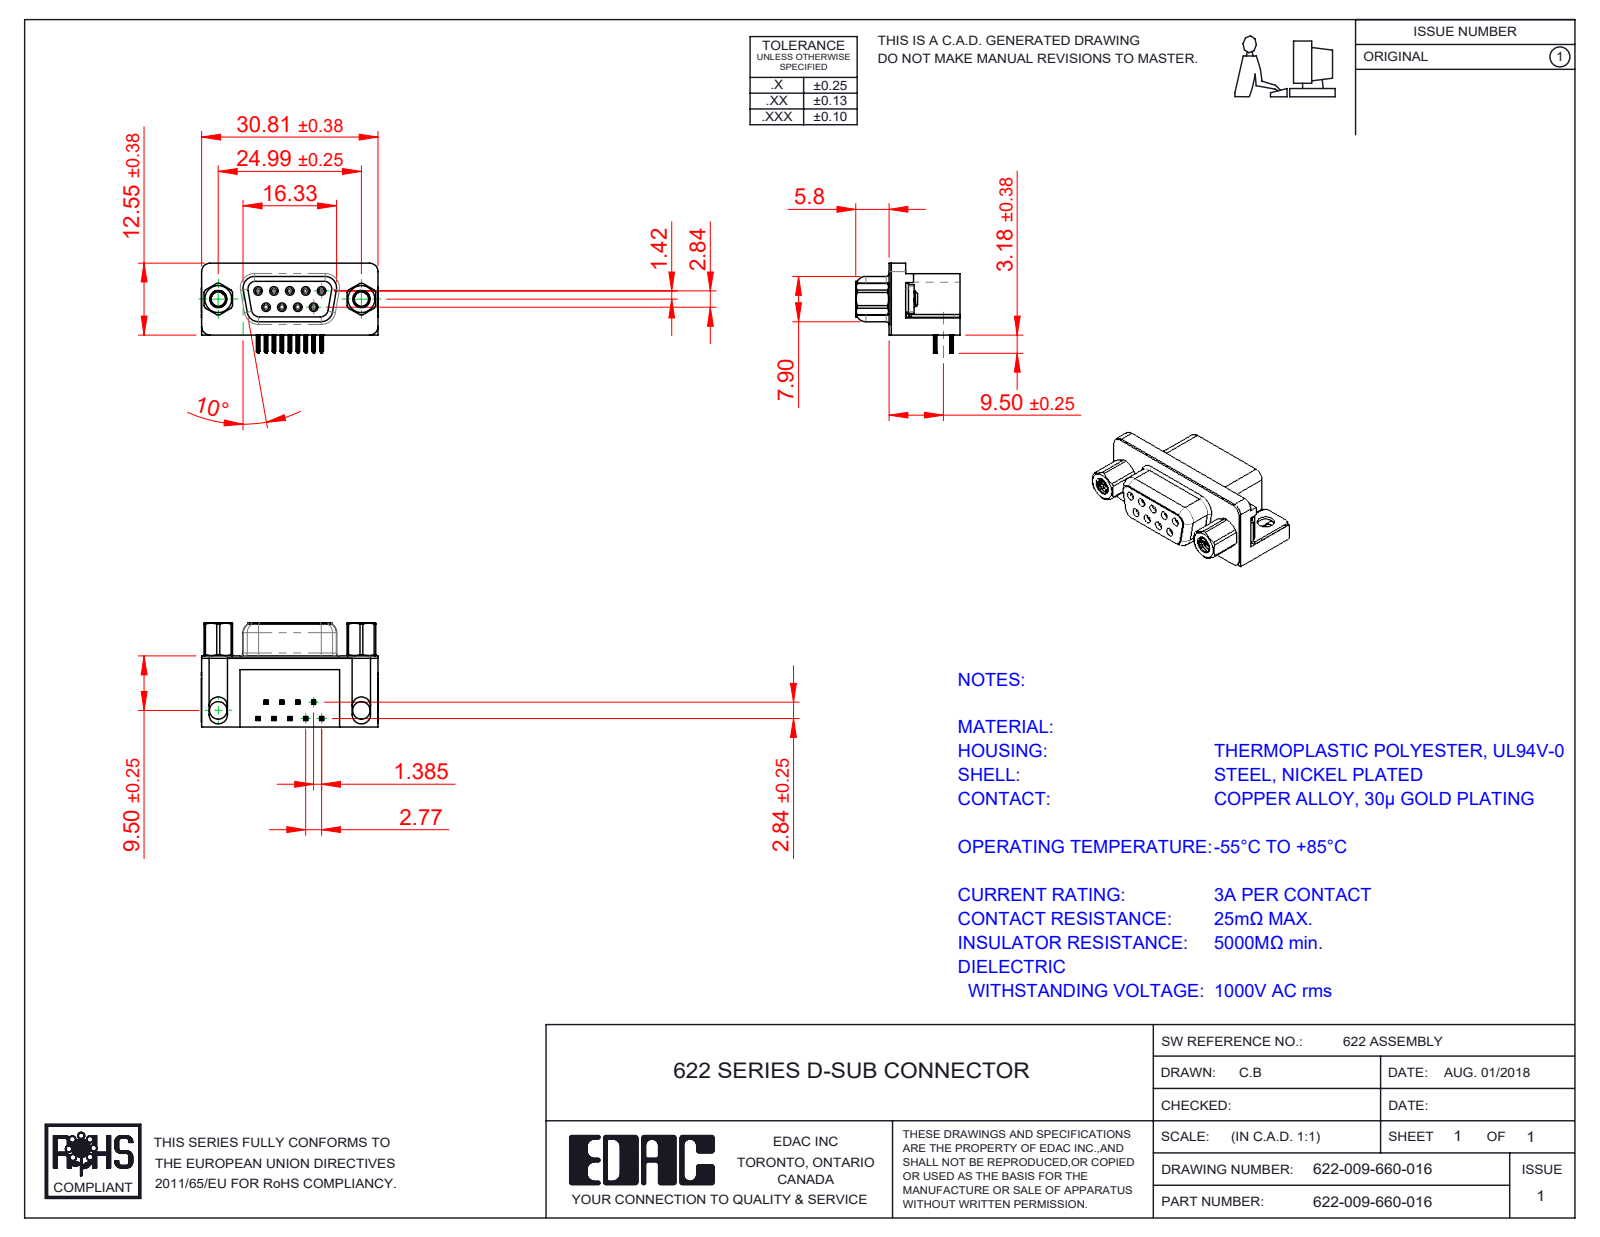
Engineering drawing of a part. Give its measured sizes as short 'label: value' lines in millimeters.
name: 622 Shell_9 Socket; 622 Contact Top; 622 Thru Hole Board Mount; 622-009-660-016 (+3 more)
written by: SolidWorks 2016 (CONFIG_CONTROL_DESIGN)
unit: mm
bodies: 15 solids, 1570 faces (682 planar, 420 cylindrical, 468 other)
size: 30.89 × 18.2 × 15.73
volume: 3 718 mm³; area: 5 064 mm²
holes: 9× ⌀0.8, 9× ⌀0.9, 2× ⌀2.5, 2× ⌀3.05, 2× ⌀4, 2× ⌀4.8, 2× ⌀5
bosses: 9× ⌀1.2, 2× ⌀4.9, 2× ⌀4.75, 2× ⌀3.9
rounds: 72× R0.1, 36× R0.15, 18× R0.35, 18× R1, 9× R0.34, 8× R0.25, 8× R1.35, 8× R1.6
face distances: 0.4, 12, 12.4, 0.35, 2.9, 2.5, 6.2, 10.34, 0.5, 9.5
hole spacings: 3.16, 2.77, 5.54, 5.03, 5.04, 8.31, 7.48, 7.49
